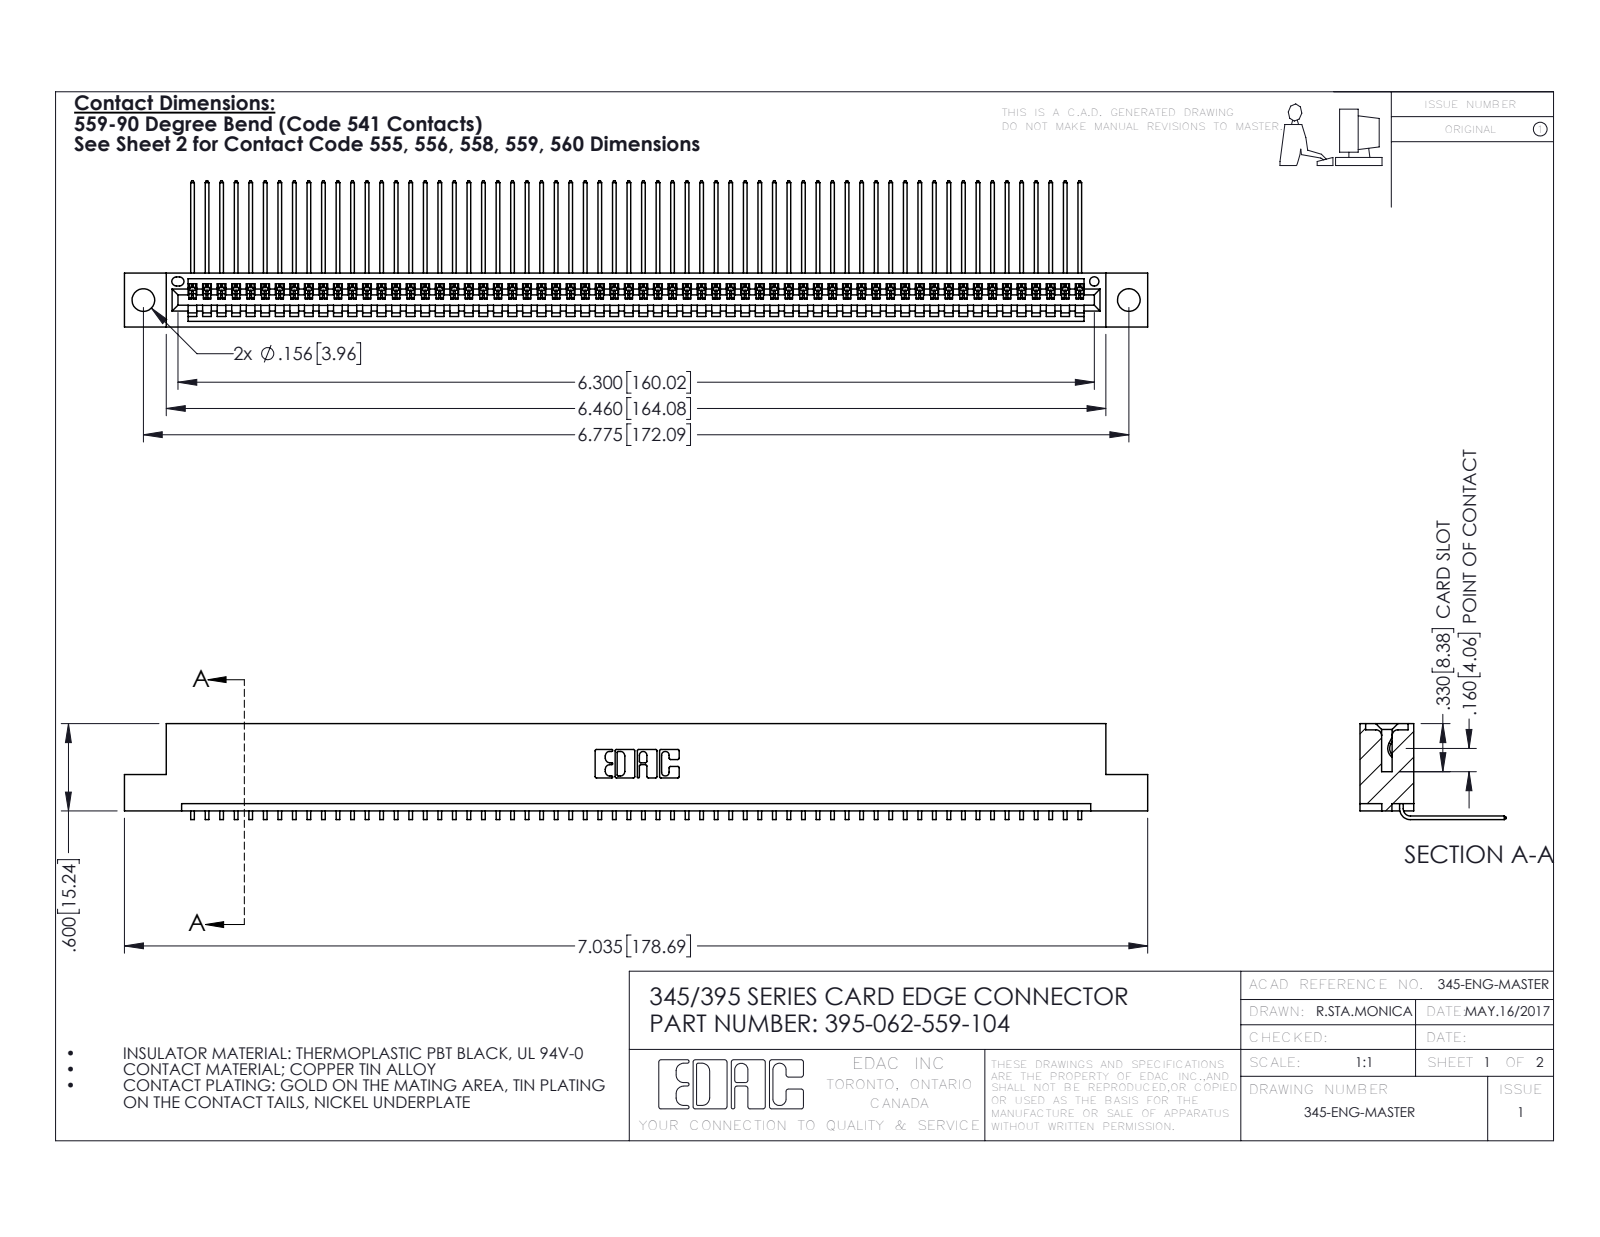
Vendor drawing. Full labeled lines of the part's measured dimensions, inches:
Part name (STEP PRODUCT): 395-062-559-104; 345-292-001_558 559 Tail - 1; 345 Part_Flush Mounting Lugs - 0.156 Dia-TH
STEP written by: SolidWorks 2016 (CONFIG_CONTROL_DESIGN)
Units: inches
Bodies: 63 solids, 3846 faces (2684 planar, 1162 cylindrical, 0 other)
Overall size (bounding box): 7.035 × 1.005 × 0.659
Volume: 1.053 in³ · Surface area: 37.55 in²
Round holes (diameter × count): ⌀0.156 ×2, ⌀0.064 ×1
Partial cylindrical surfaces — rounded edges, fillets, slot ends (radius × count): R0.006 ×124, R0.01 ×22, R0.007 ×6, R0.031 ×6, R0.026 ×3, R0.031 ×2, R0.04 ×2, R0.014 ×1
Main face-to-face distances: 0.298, 0.072, 0.37, 0.2, 0.098, 0.272, 0.025, 0.225, 0.149, 0.072
Hole centre spacings: 0.27, 6.539, 6.775
